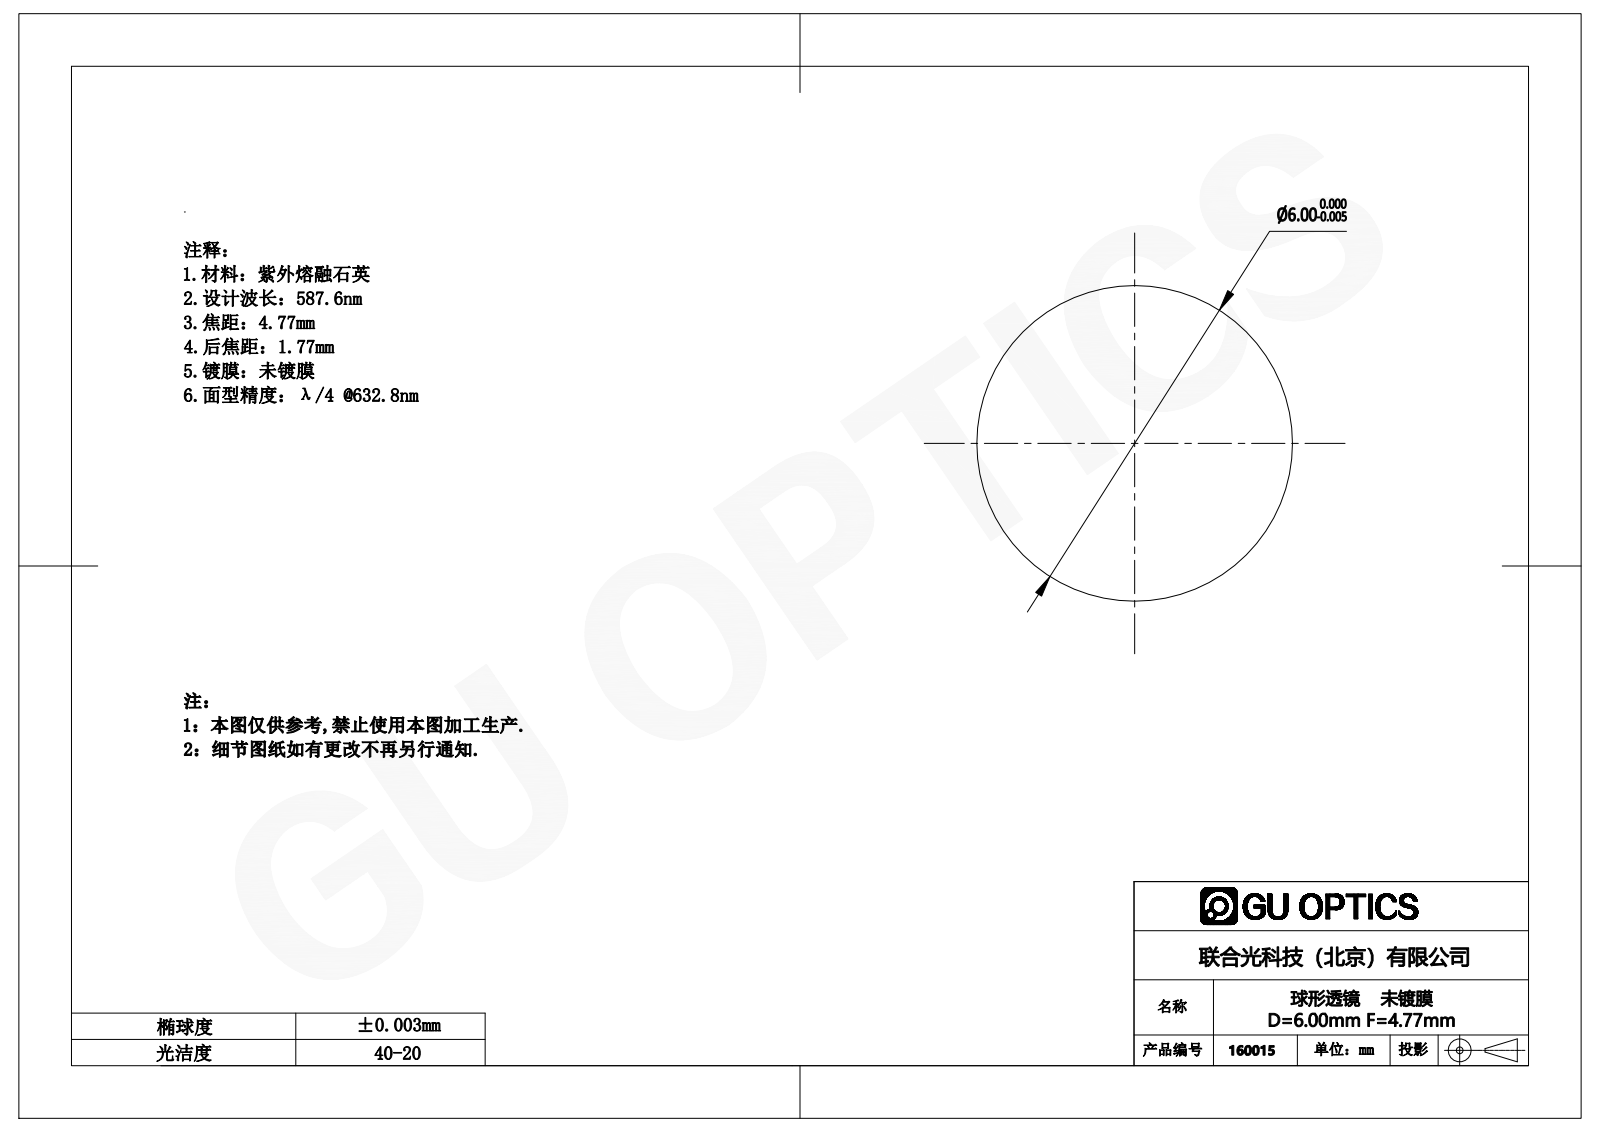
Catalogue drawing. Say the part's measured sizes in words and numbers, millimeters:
The part is named "160005". Its 3-D file was written by "SolidWorks 2016 (CONFIG_CONTROL_DESIGN)". It is 1 solid with 2 faces: 0 planar, 0 cylindrical and 2 other. Overall it measures 6 by 6 by 6 millimeters. Its volume is 113 cubic millimeters and its surface area 113 square millimeters.
